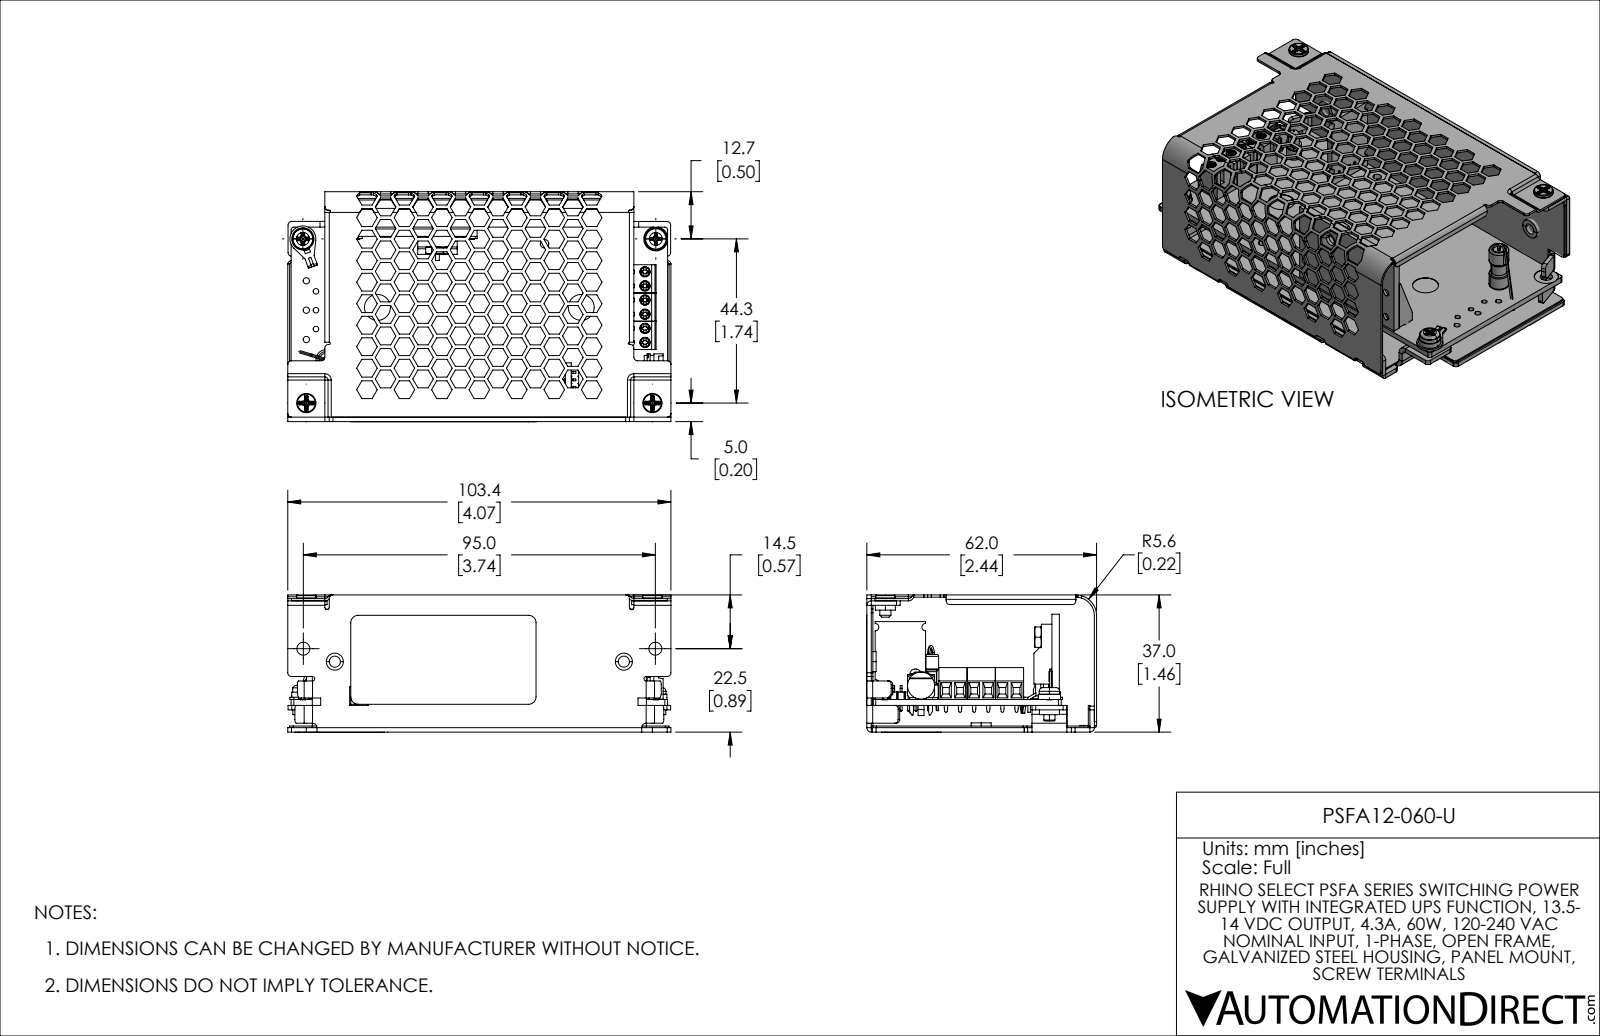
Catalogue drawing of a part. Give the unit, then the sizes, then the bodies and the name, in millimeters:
Units: millimetres
Overall size (bounding box): 103.4 × 62.1 × 37.1
Round holes (diameter × count): ⌀3 ×9, ⌀1.3 ×6, ⌀1.7 ×6, ⌀2.7 ×6, ⌀2 ×4, ⌀3.3 ×4, ⌀6.5 ×4, ⌀1.5 ×3, ⌀1.7 ×3, ⌀2.3 ×2, ⌀3.2 ×2, ⌀3.5 ×2
Round bosses / shafts (diameter × count): ⌀5.4 ×8, ⌀2.7 ×6, ⌀2.6 ×4, ⌀6 ×2, ⌀5.5 ×2, ⌀5.2 ×2, ⌀0.7 ×2, ⌀5.3 ×1
Partial cylindrical surfaces — rounded edges, fillets, slot ends (radius × count): R1 ×85, R0.1 ×64, R1.2 ×13, R0.6 ×9, R0.1 ×6, R0.3 ×6, R0.5 ×6, R0.8 ×6
Main face-to-face distances: 1.2, 0.4, 1.6, 1.6, 6, 7.6, 7.2, 8.8, 7.2, 5.6
Hole centre spacings: 3.8, 4, 71.7, 7.6, 7.9, 55, 74.2, 2.7
Volume: 32 220 mm³ · Surface area: 72 770 mm²
Bodies: 26 solids, 3381 faces (2565 planar, 497 cylindrical, 319 other)
Part name (STEP PRODUCT): PSFA12-060-U
STEP written by: SolidWorks 2021 (AUTOMOTIVE_DESIGN)
